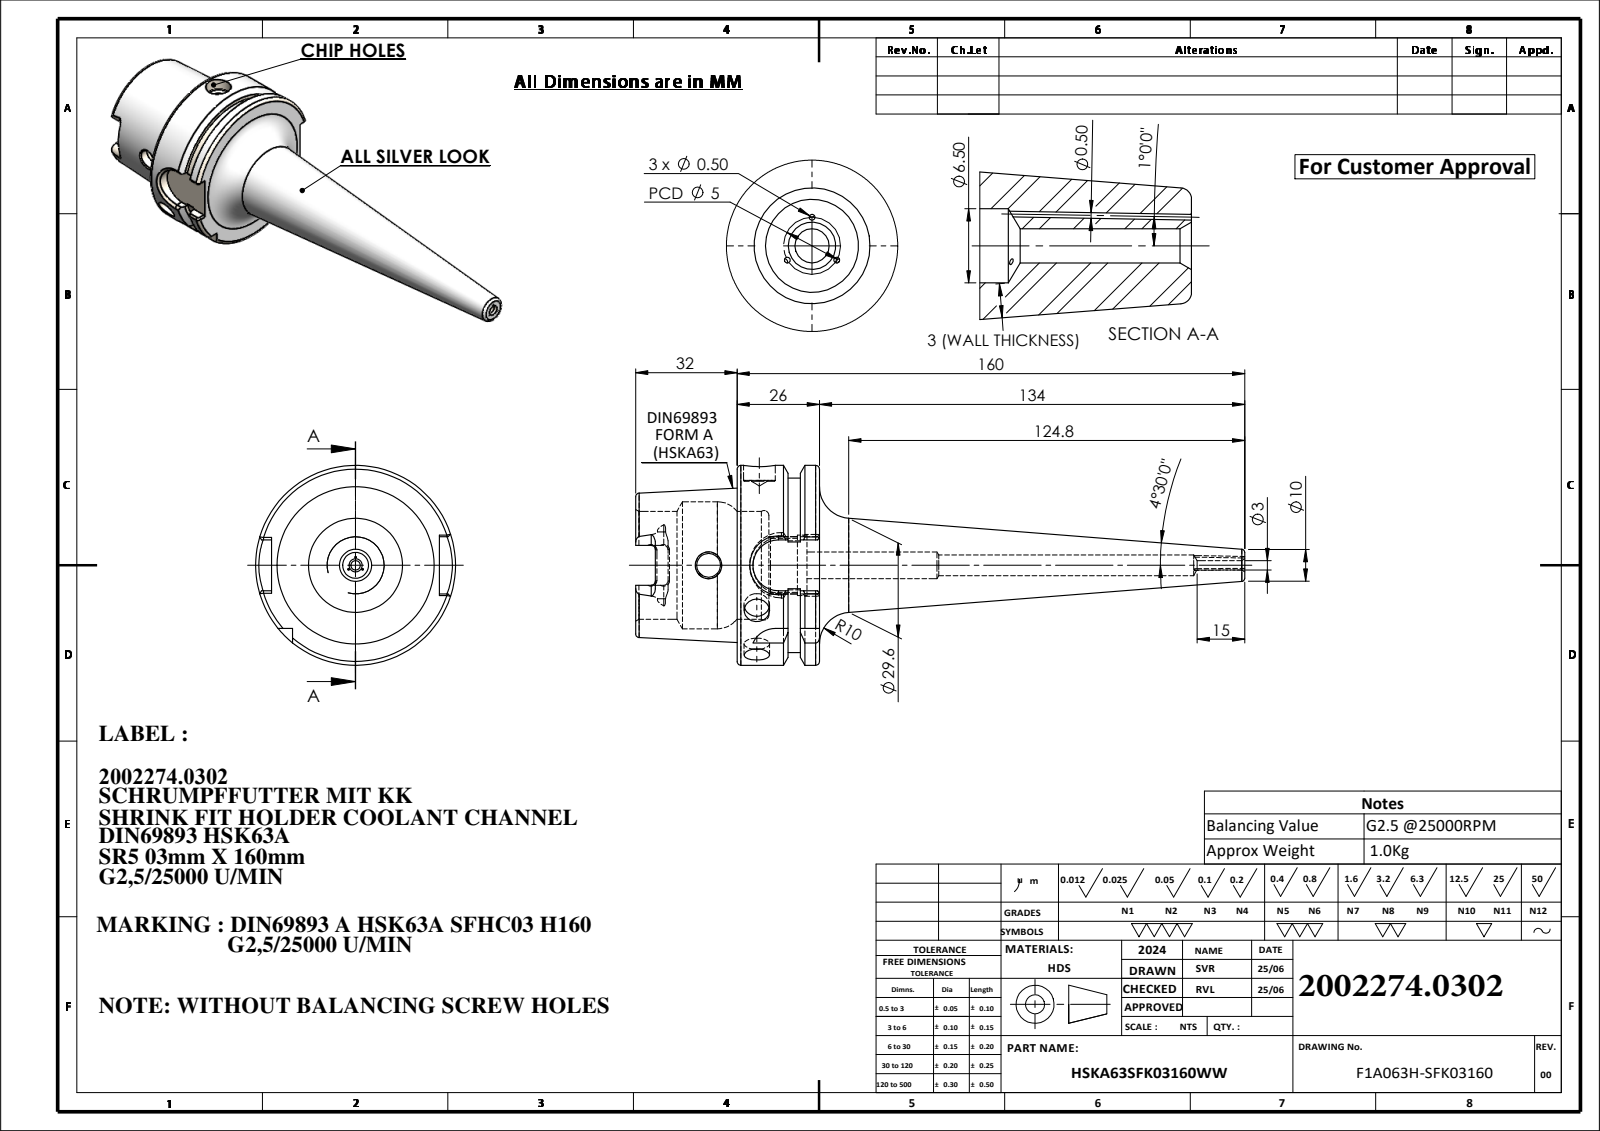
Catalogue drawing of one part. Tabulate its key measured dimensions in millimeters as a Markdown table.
| quantity | value |
| --- | --- |
| part name | F1A063H-SFK03160 |
| STEP written by | SolidWorks 2024 (CONFIG_CONTROL_DESIGN) |
| units | millimeters |
| bodies | 1 solid, 172 faces (49 planar, 55 cylindrical, 68 other) |
| overall size | 192 × 63 × 63 |
| volume | 126 243 mm³ |
| surface area | 32 954 mm² |
| round holes (diameter × count) | 0.5 × 3, 8 × 2, 2.99 × 1, 6.5 × 1, 7.5 × 1, 8.4 × 1, 10 × 1, 17 × 1, 19 × 1, 34 × 1, 40 × 1 |
| round bosses / shafts (diameter × count) | 63 × 1, 55 × 1 |
| partial cylindrical surfaces (radius × count) | 1.3 × 6, 2.88 × 4, 8 × 2, 9 × 1 |
| main face-to-face distances | 25.95, 10, 15.95, 32, 42, 57.95, 52.9, 54, 22, 12 |
